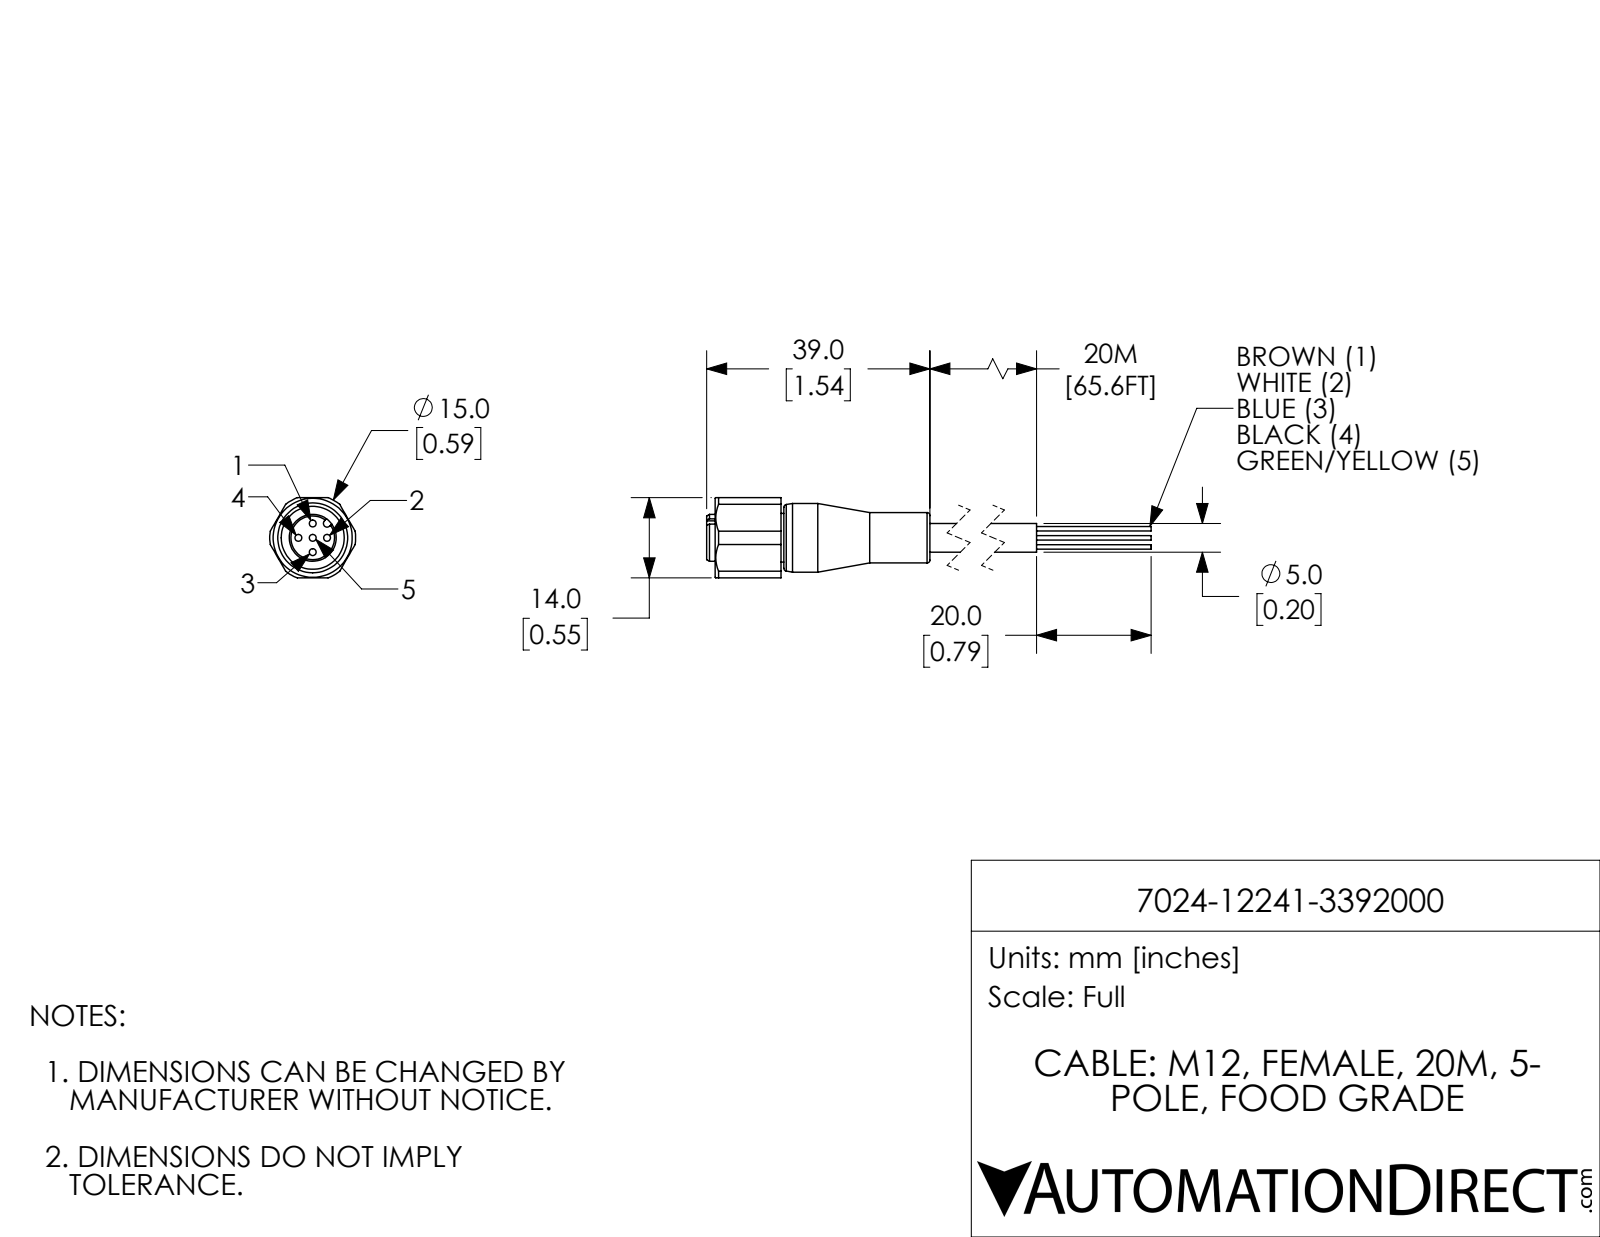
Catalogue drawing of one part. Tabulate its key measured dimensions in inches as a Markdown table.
| quantity | value |
| --- | --- |
| part name | 7024-12241-3392000 |
| STEP written by | SolidWorks 2018 (AUTOMOTIVE_DESIGN) |
| units | inches |
| bodies | 1 solid, 80 faces (26 planar, 39 cylindrical, 15 other) |
| overall size | 3.063 × 0.591 × 0.551 |
| volume | 0.252 in³ |
| surface area | 4.458 in² |
| round holes (diameter × count) | 0.047 × 5, 0.433 × 1 |
| round bosses / shafts (diameter × count) | 0.03 × 5, 0.472 × 1, 0.346 × 1, 0.335 × 1, 0.323 × 1, 0.197 × 1 |
| partial cylindrical surfaces (radius × count) | 0.026 × 1, 0.295 × 1 |
| main face-to-face distances | 0.551, 0.157, 0.354, 0.512, 0.059, 0.295, 0.453, 0.531, 0.472, 0.177 |
| hole center spacings | 0.098, 0.139, 0.197 |
